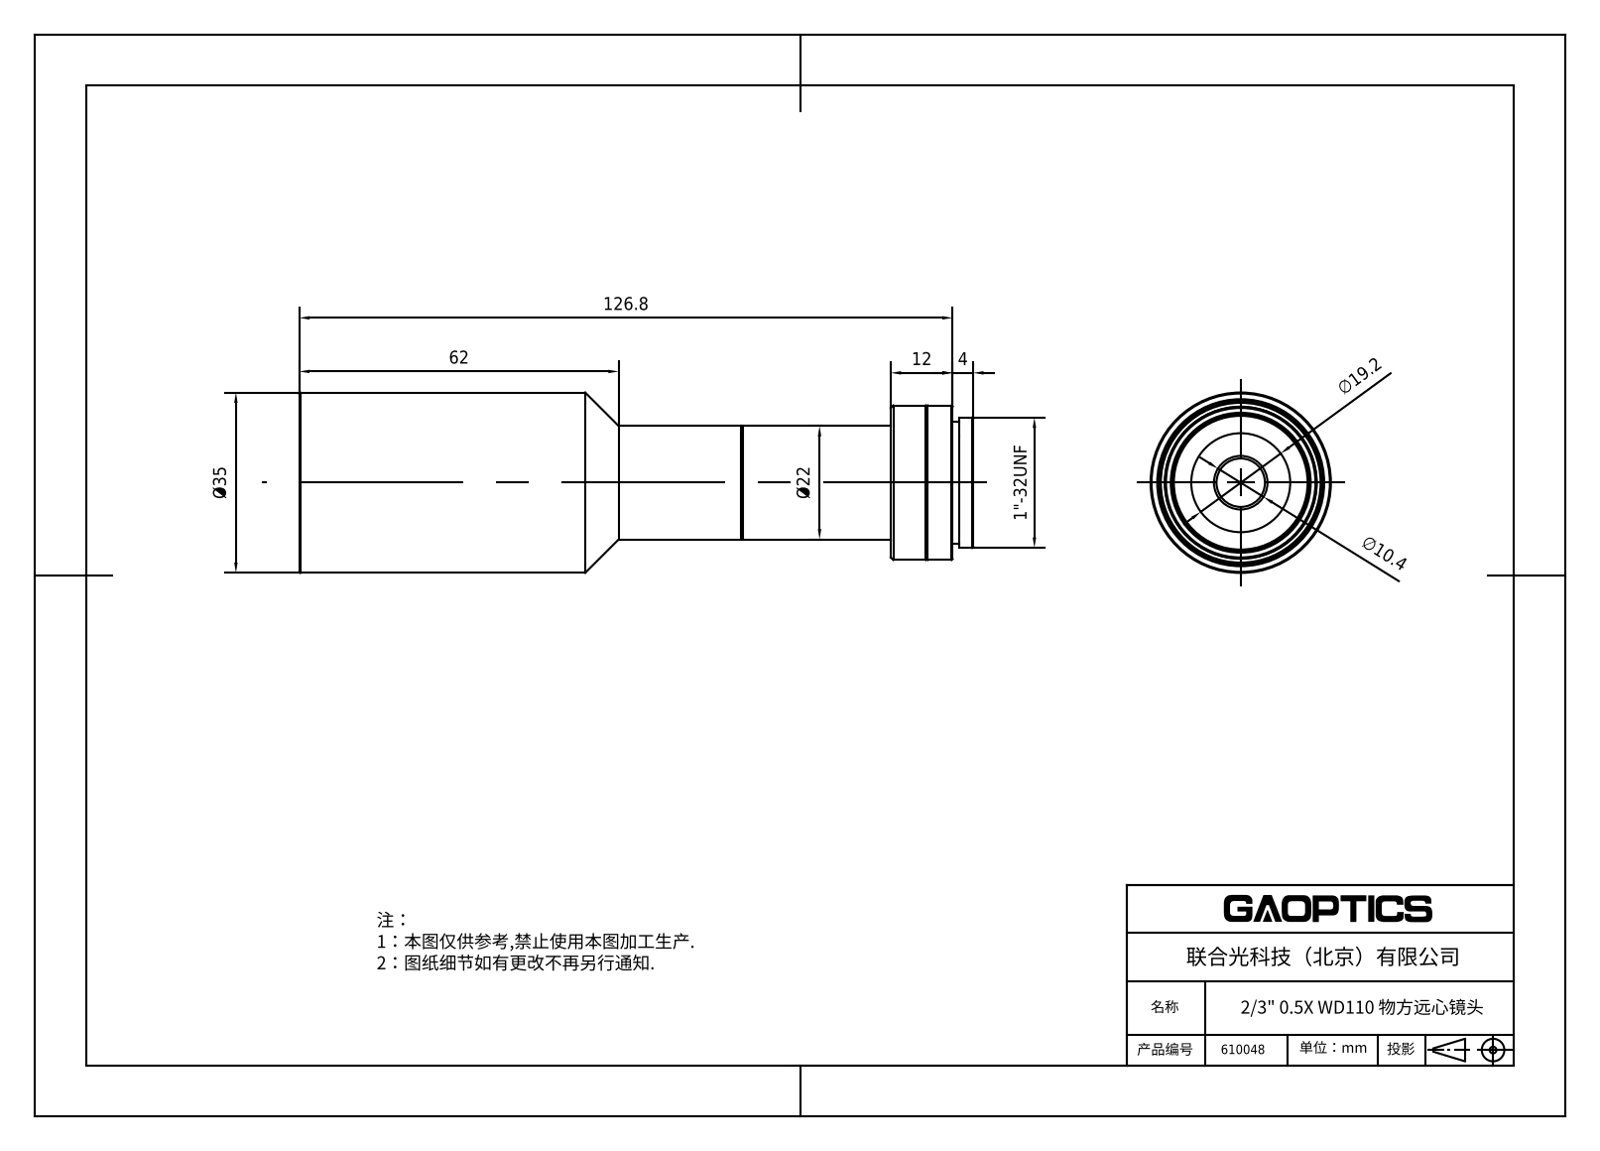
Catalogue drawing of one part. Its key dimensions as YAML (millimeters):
part_name: "610048"
step_written_by: "SolidWorks 2020 (CONFIG_CONTROL_DESIGN)"
units: millimeters
bodies: {solids: 3, faces: 196, planar: 30, cylindrical: 75, other: 91}
overall_size: [130.8, 35, 35]
volume: 75414
surface_area: 19287
round_holes:
  - {diameter: 1.6, count: 1}
  - {diameter: 2.2, count: 1}
  - {diameter: 4, count: 1}
  - {diameter: 14.2, count: 1}
  - {diameter: 15, count: 1}
  - {diameter: 15.6, count: 1}
  - {diameter: 17.3, count: 1}
  - {diameter: 19, count: 1}
  - {diameter: 22.2, count: 1}
  - {diameter: 29, count: 1}
  - {diameter: 29.4, count: 1}
  - {diameter: 31, count: 1}
round_bosses_or_shafts:
  - {diameter: 35, count: 1}
  - {diameter: 30, count: 1}
  - {diameter: 25.26, count: 1}
  - {diameter: 23.76, count: 1}
  - {diameter: 22, count: 1}
  - {diameter: 18, count: 1}
  - {diameter: 17, count: 1}
partial_cylinders:
  - {radius: 1, count: 2}
  - {radius: 2, count: 1}
  - {radius: 3, count: 1}
face_to_face_distances: [109.58, 1, 4, 4.5, 6, 5, 7, 114.58, 12, 102.58]
